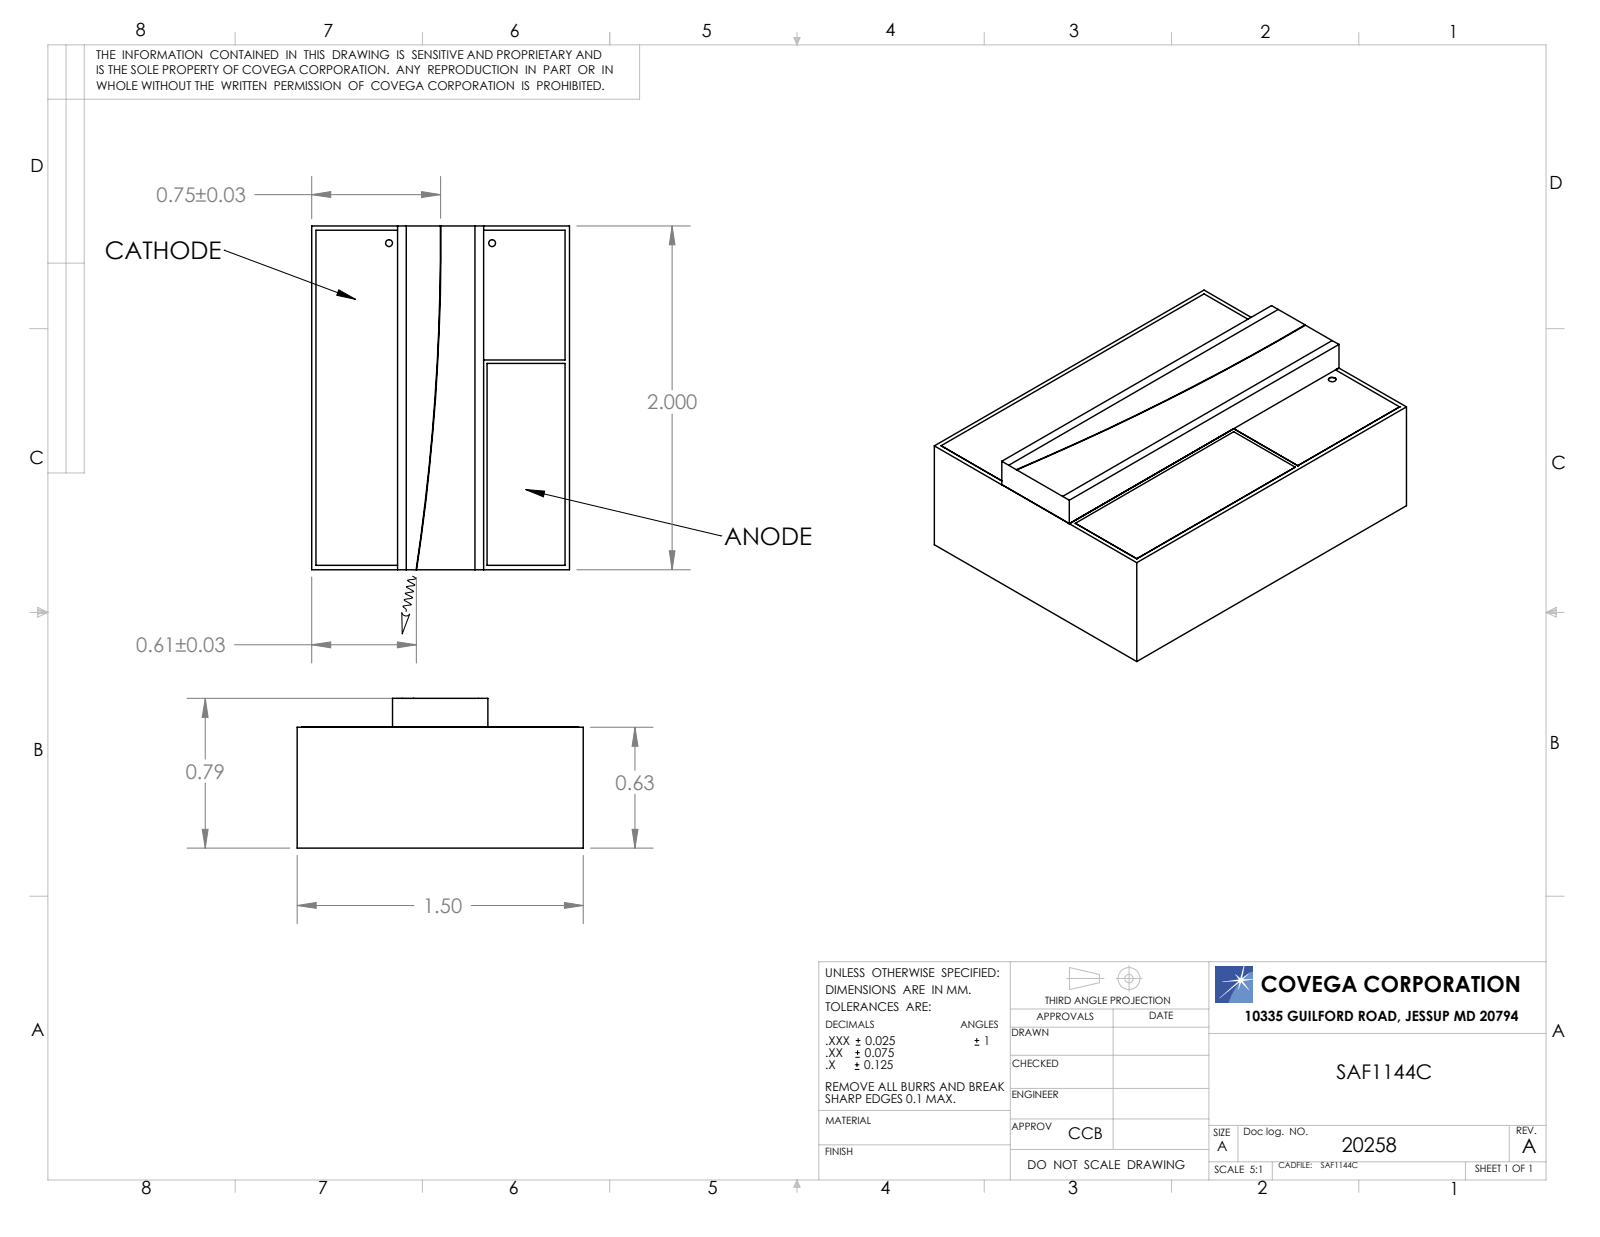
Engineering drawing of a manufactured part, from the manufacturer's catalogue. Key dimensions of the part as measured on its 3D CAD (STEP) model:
Part name (STEP PRODUCT): 32066-000; 31144-xxx; 20258
STEP written by: SolidWorks 2009 (AUTOMOTIVE_DESIGN)
Units: millimetres
Bodies: 2 solids, 42 faces (38 planar, 4 cylindrical, 0 other)
Overall size (bounding box): 2 × 1.5 × 0.79
Volume: 2 mm³ · Surface area: 13 mm²
Main face-to-face distances: 0.64, 1.5, 2, 0.79, 0.5, 1, 0.48, 1.48, 0.98, 0.47
Hole centre spacings: 0.6
